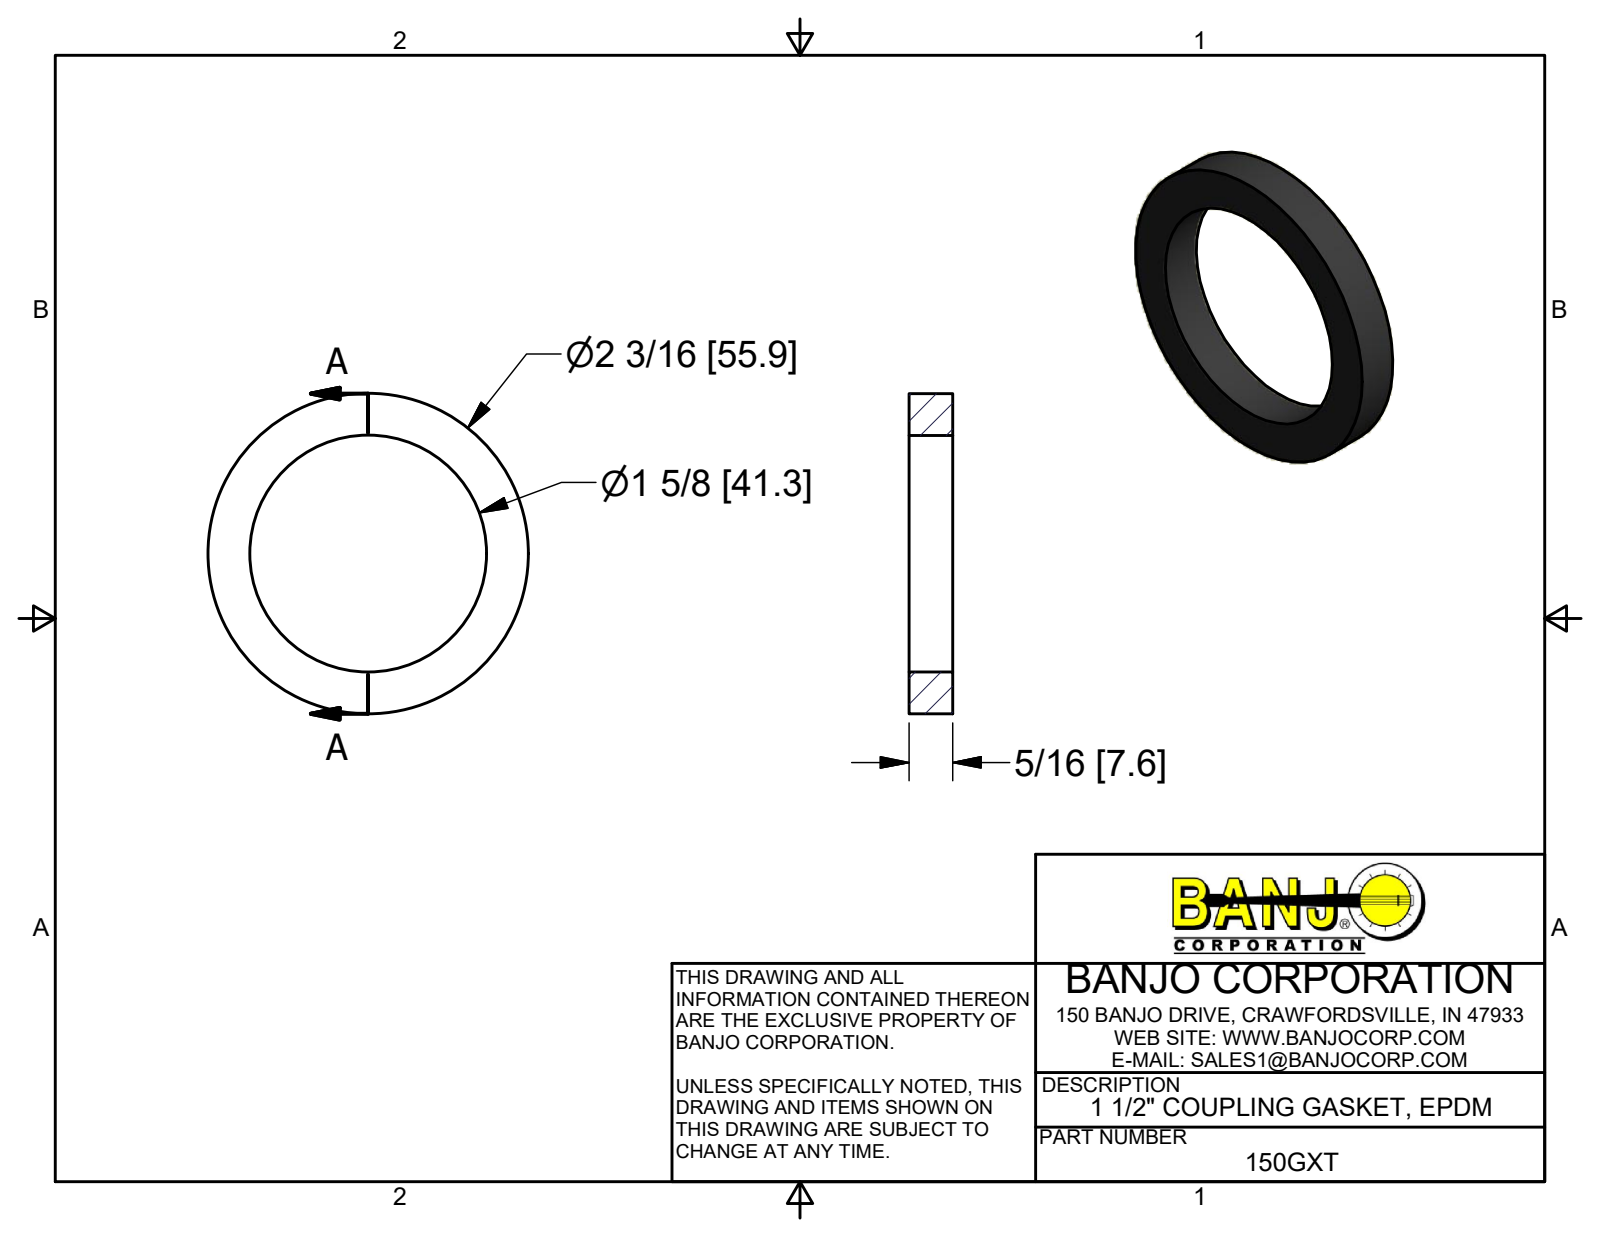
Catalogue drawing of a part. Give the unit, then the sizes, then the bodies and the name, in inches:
Units: inches
Overall size (bounding box): 2.2 × 2.2 × 0.3
Round holes (diameter × count): ⌀1.625 ×1
Round bosses / shafts (diameter × count): ⌀2.2 ×1
Main face-to-face distances: 0.3
Volume: 0.518 in³ · Surface area: 7.06 in²
Bodies: 1 solid, 4 faces (2 planar, 2 cylindrical, 0 other)
Part name (STEP PRODUCT): 150GXT
STEP written by: Autodesk Inventor 2017 (AUTOMOTIVE_DESIGN)
